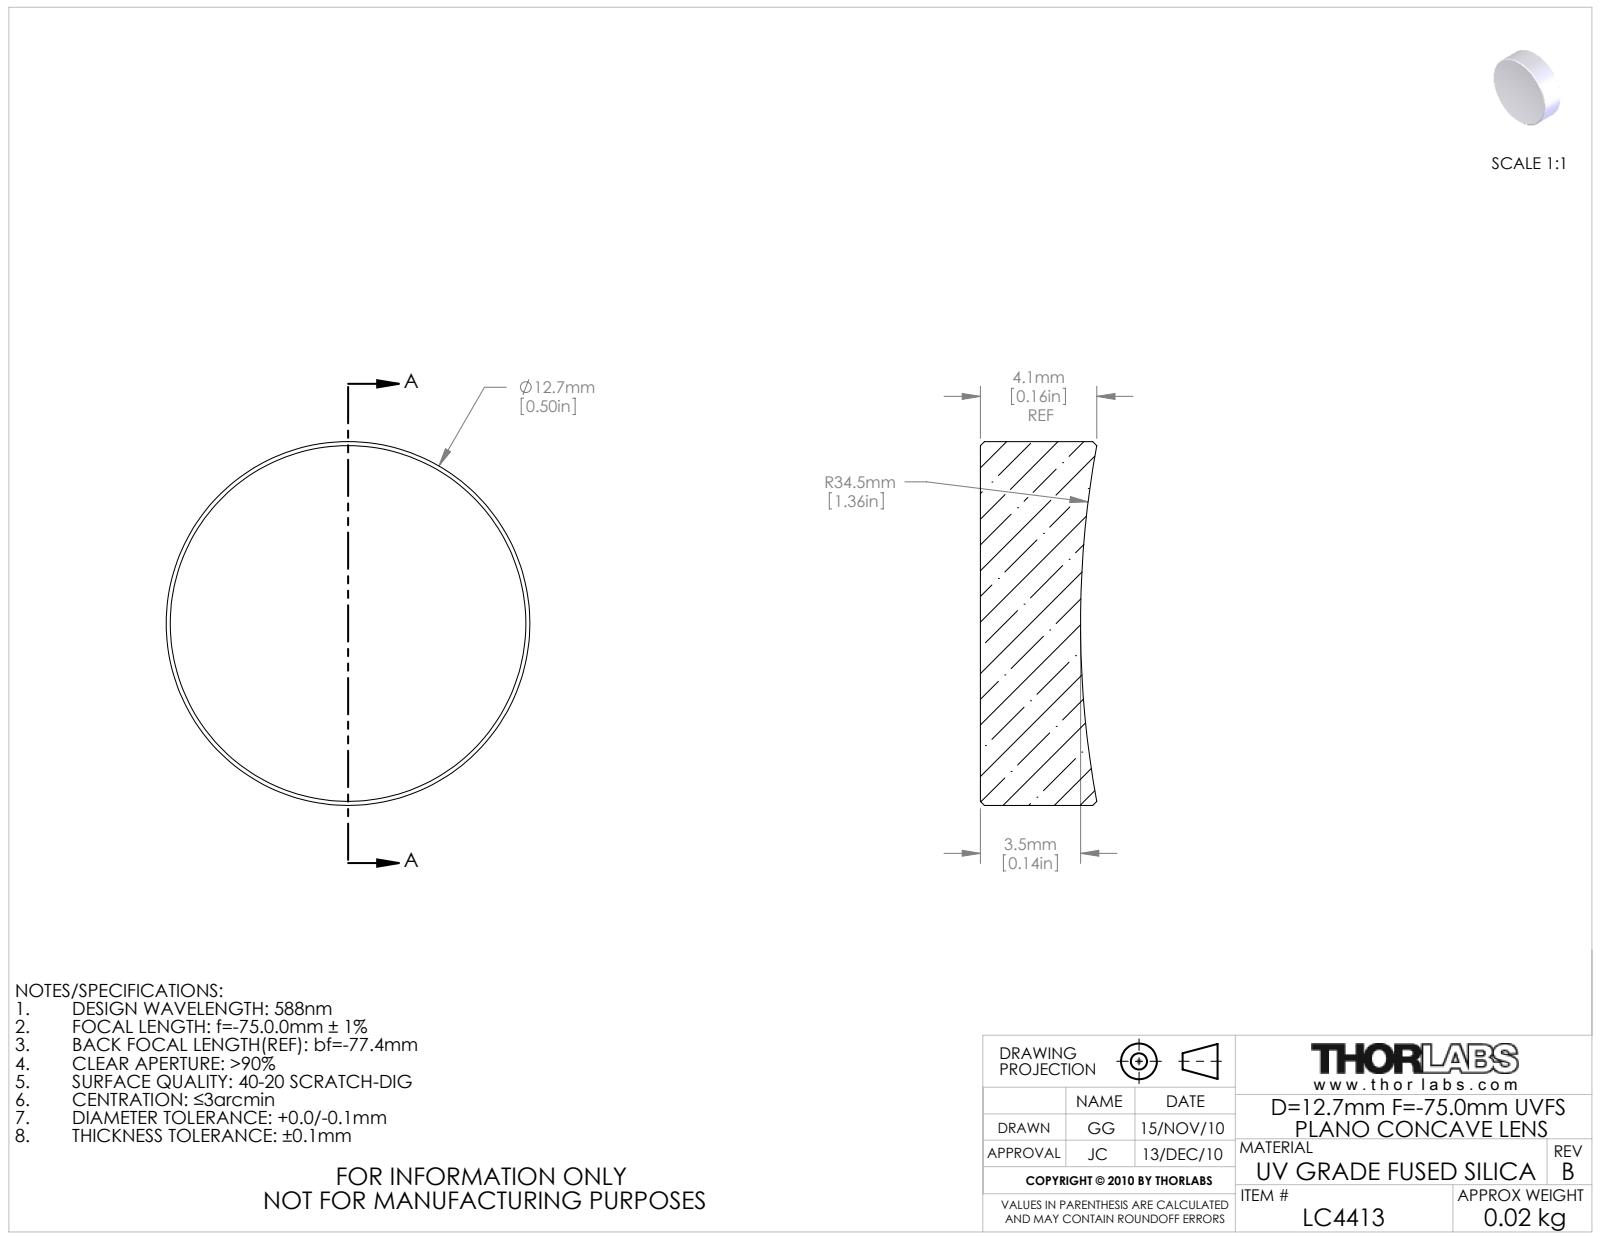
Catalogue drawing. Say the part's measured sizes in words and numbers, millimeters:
The part is named "3498-E0W". Its 3-D file was written by "SolidWorks 2009 (AUTOMOTIVE_DESIGN)". It is 1 solid with 9 faces: 1 planar, 2 cylindrical and 6 other. Overall it measures 12.7 by 12.7 by 4.06 millimeters. Its volume is 480 cubic millimeters and its surface area 410 square millimeters. Round bosses or shafts: 1 of diameter 12.7.
